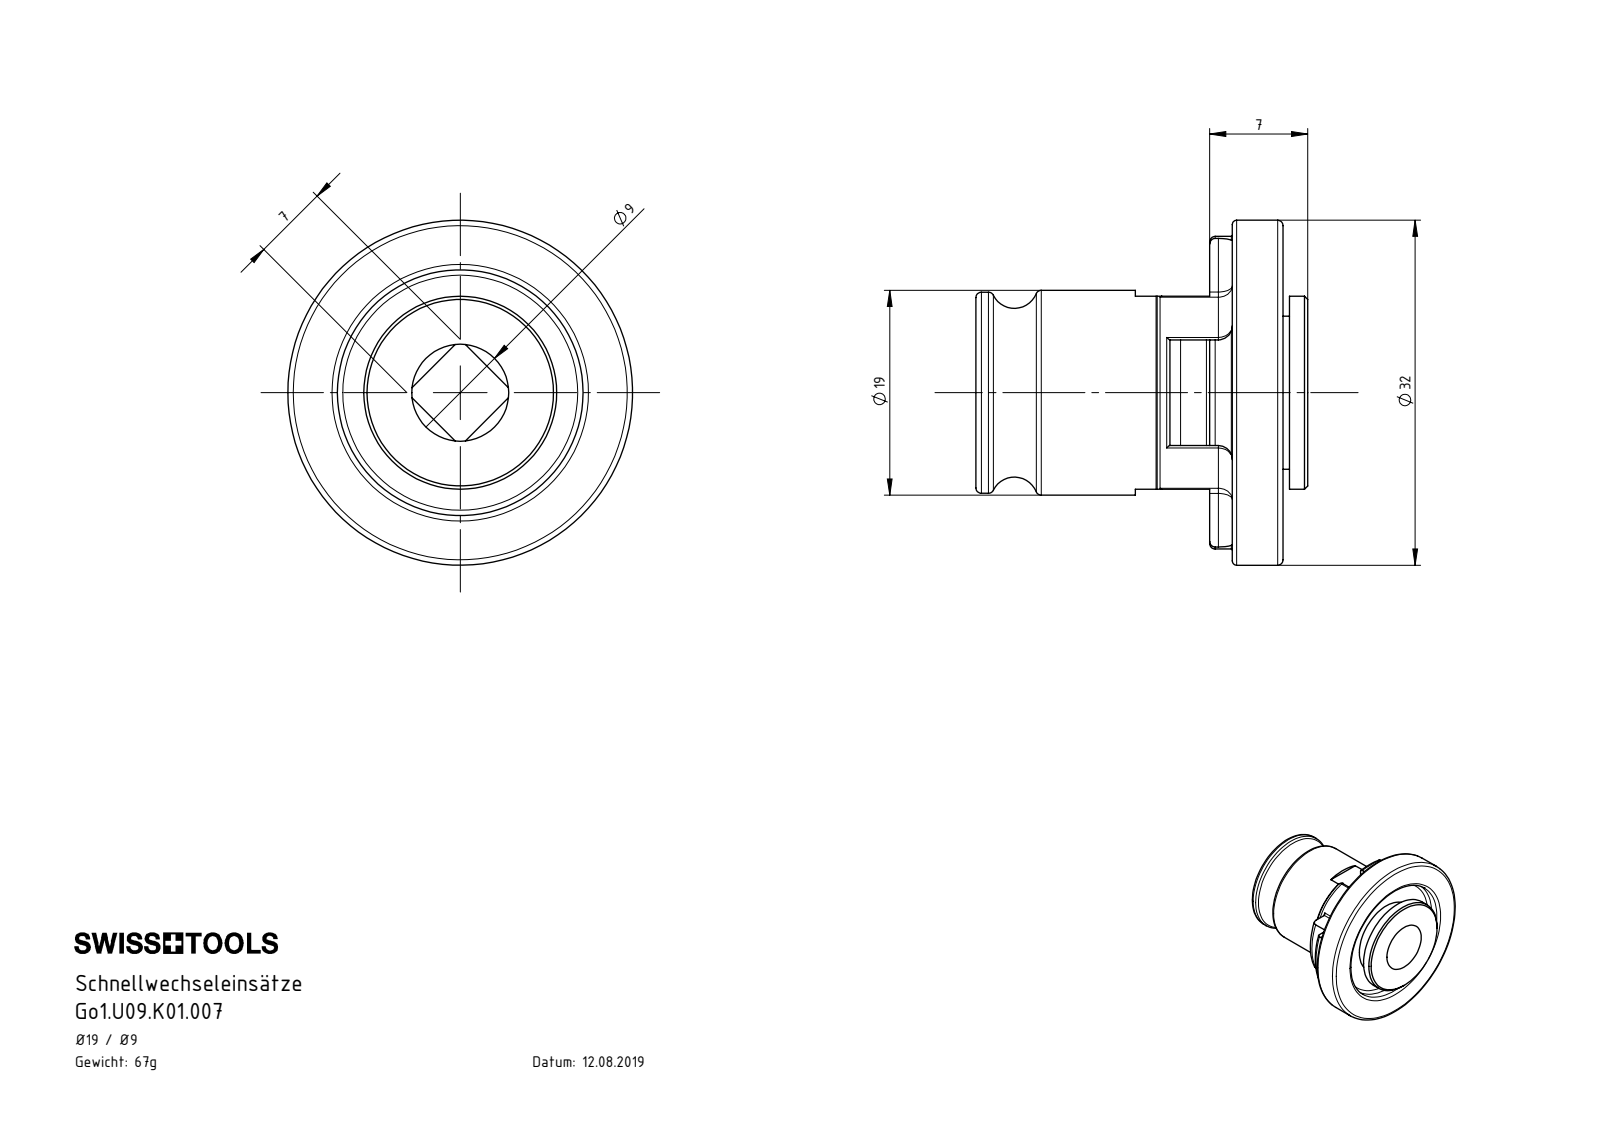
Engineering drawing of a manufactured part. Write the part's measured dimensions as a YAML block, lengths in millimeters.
part_name: "Go1.U09.K01.007"
step_written_by: "SolidWorks 2017 (AUTOMOTIVE_DESIGN)"
units: millimeters
bodies: {solids: 1, faces: 110, planar: 36, cylindrical: 32, other: 42}
overall_size: [32, 32, 30.8]
volume: 8564
surface_area: 4888
round_holes:
  - {diameter: 9, count: 1}
  - {diameter: 11.4, count: 1}
  - {diameter: 22.8, count: 1}
round_bosses_or_shafts:
  - {diameter: 32, count: 1}
  - {diameter: 19, count: 1}
  - {diameter: 18.65, count: 1}
  - {diameter: 18.52, count: 1}
  - {diameter: 17.9, count: 1}
  - {diameter: 14.2, count: 1}
partial_cylinders:
  - {radius: 0.5, count: 8}
  - {radius: 1.3, count: 4}
  - {radius: 12.4, count: 1}
  - {radius: 14.5, count: 1}
face_to_face_distances: [2.35, 4.7, 7, 4.65, 2.3, 23.8, 26.15, 28.5, 30.8, 29.1]
